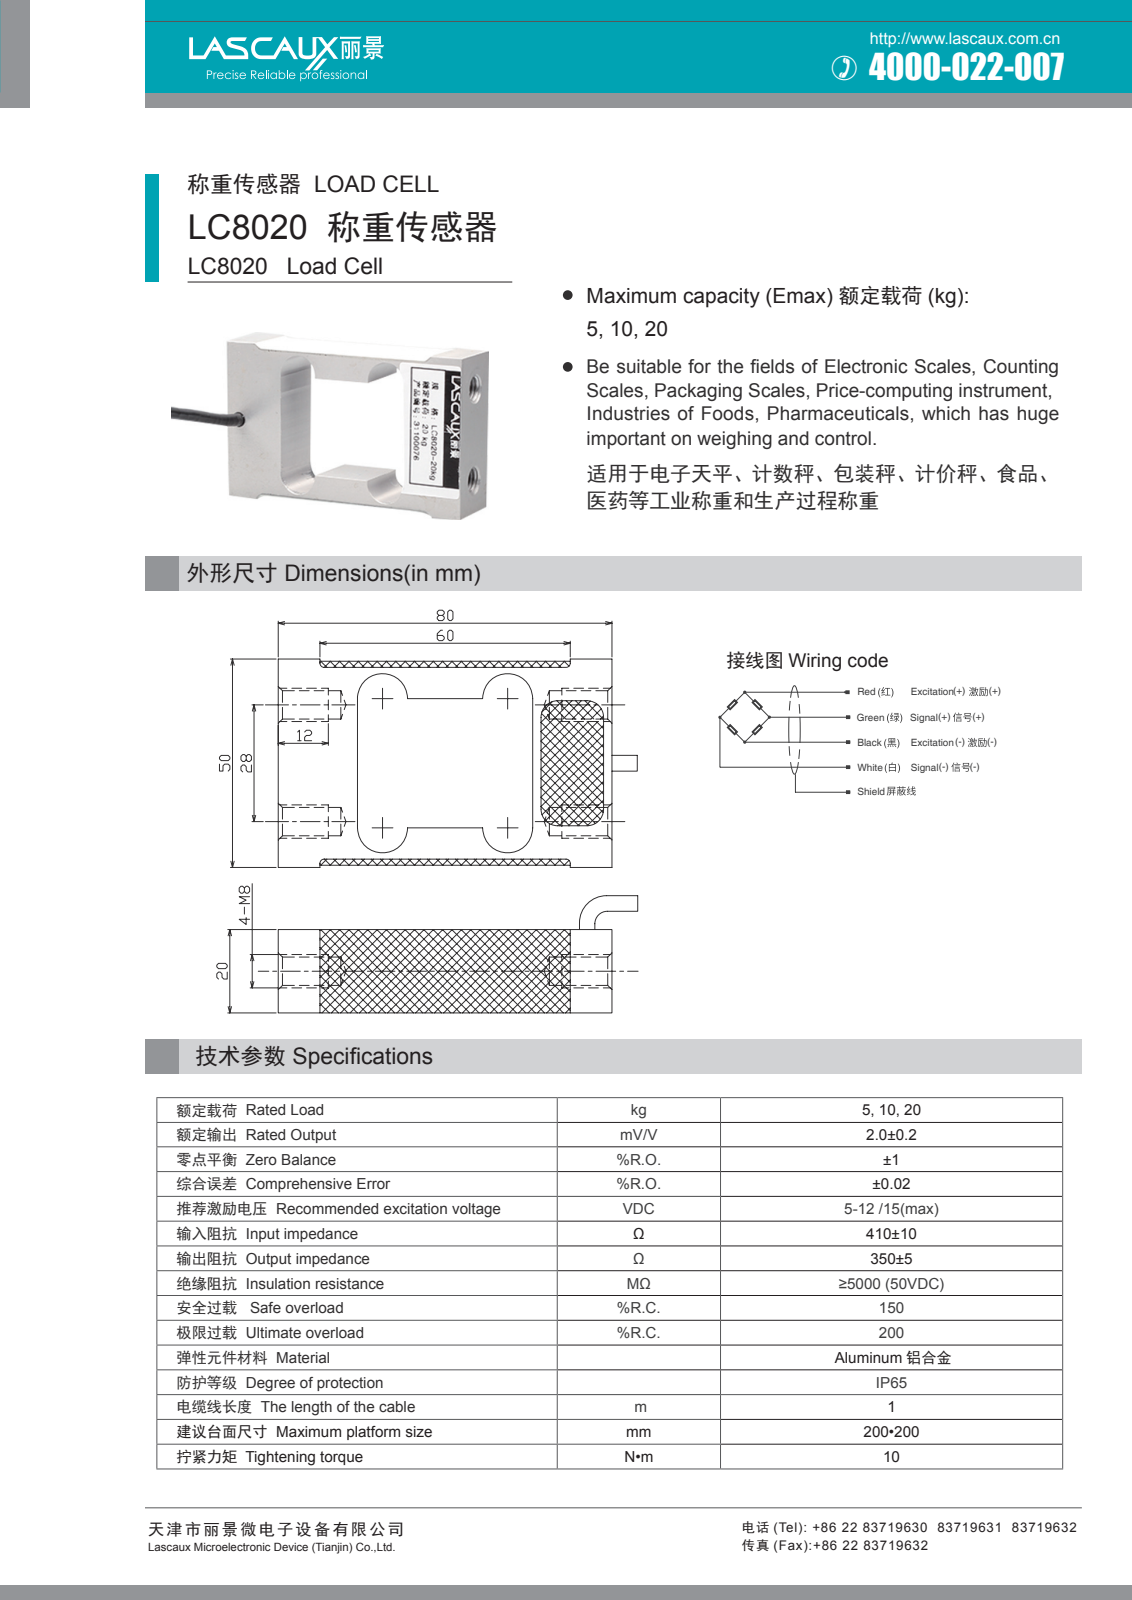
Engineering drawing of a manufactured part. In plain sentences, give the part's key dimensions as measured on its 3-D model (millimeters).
The part is named "LC8020". Its 3-D file was written by "SolidWorks 2016 (CONFIG_CONTROL_DESIGN)". It is 1 solid with 42 faces: 18 planar, 16 cylindrical and 8 other. Overall it measures 80 by 50 by 20 millimeters. Its volume is 43 233 cubic millimeters and its surface area 14 339 square millimeters. Round holes: 2 of diameter 6.8. Partial cylindrical surfaces (rounded edges, fillets, slot ends): 4 of radius 1, 4 of radius 5. The main face-to-face distances are 20, 17.5, 62.5, 46, 8, 38, 80, 10, 2, 40. The hole center spacings are 28.
